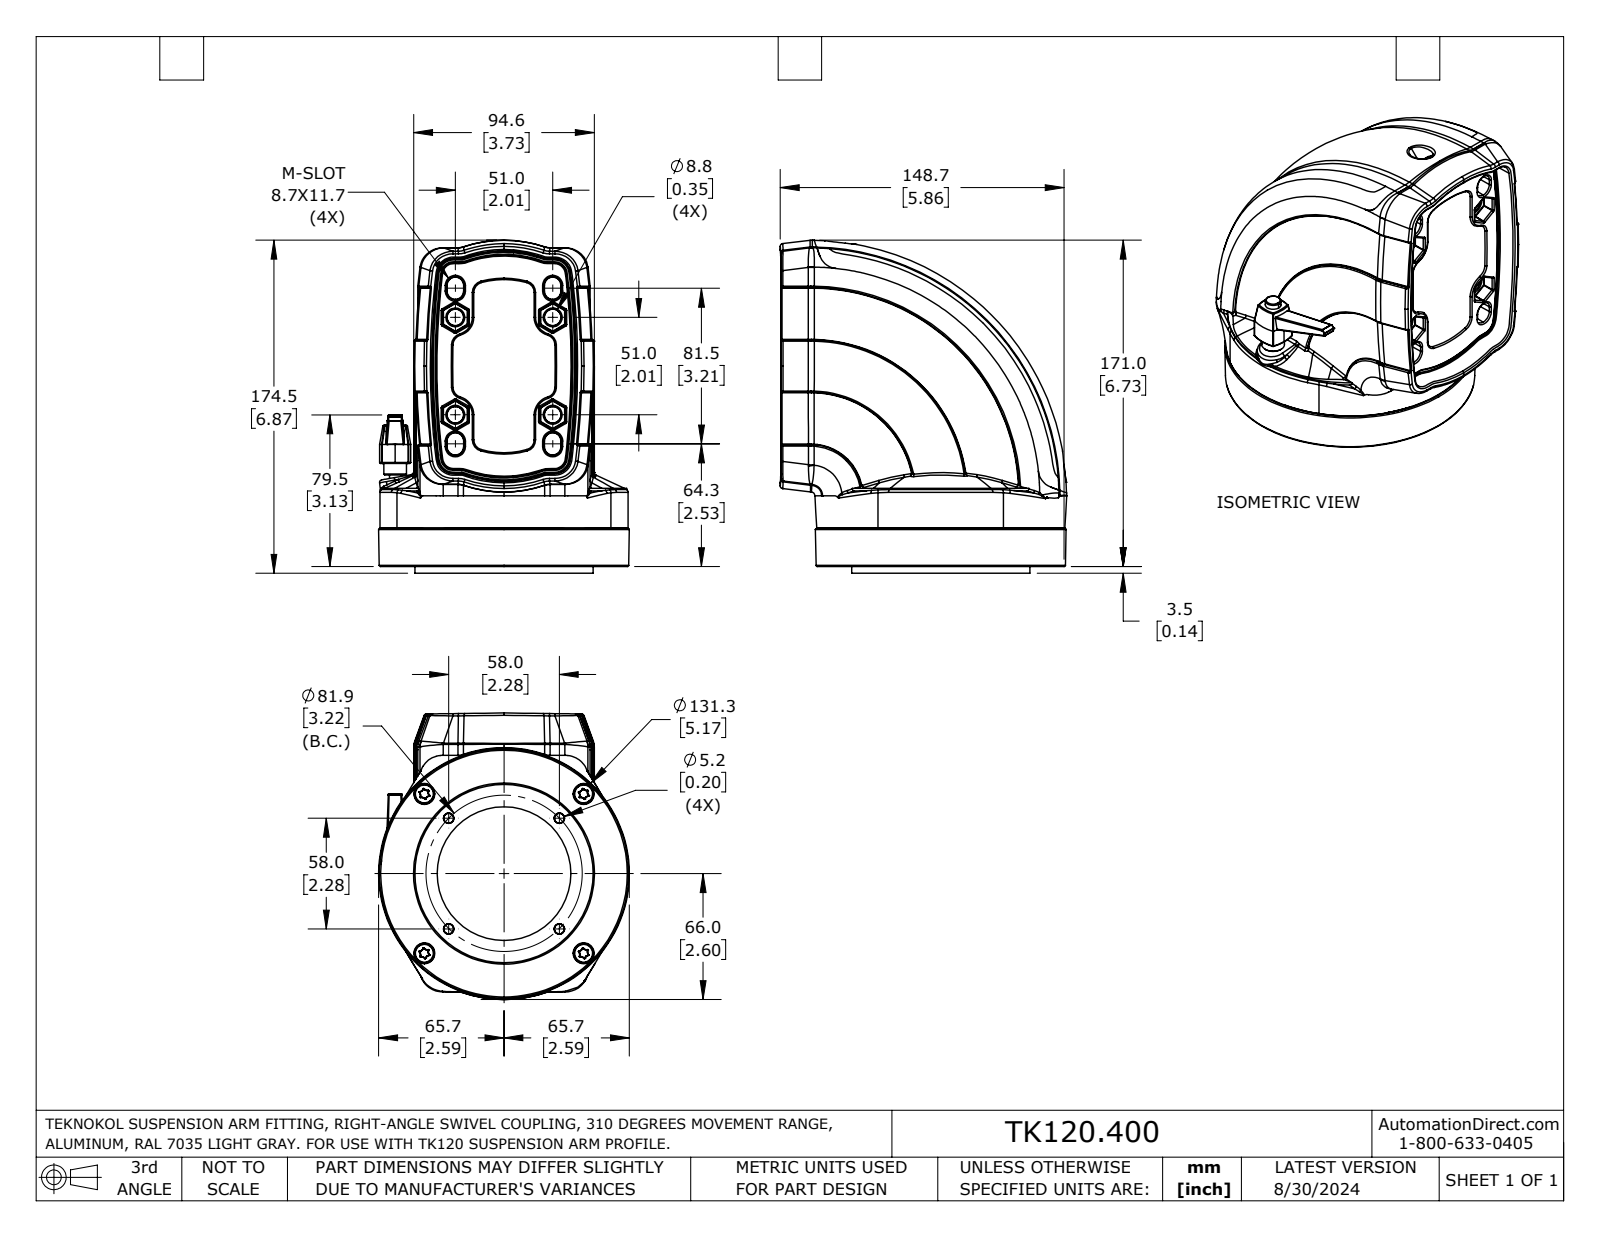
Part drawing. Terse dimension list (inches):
name: TK120.400
written by: SolidWorks 2023 (AUTOMOTIVE_DESIGN)
unit: in
bodies: 1 solid, 1261 faces (139 planar, 40 cylindrical, 1082 other)
size: 6.869 × 5.909 × 5.17
volume: 107.9 in³; area: 163.6 in²
holes: 1× ⌀2.756
bosses: 1× ⌀3.674, 1× ⌀0.469, 1× ⌀0.237, 1× ⌀0.236
rounds: 6× R0.197, 4× R0.097, 2× R0.029, 2× R5.112, 1× R0.161, 1× R0.354, 1× R0.393, 1× R0.891
face distances: 0.222, 0.029, 0.138, 0.36, 0.452, 0.423, 0.236, 0.03, 0.422, 1.004
